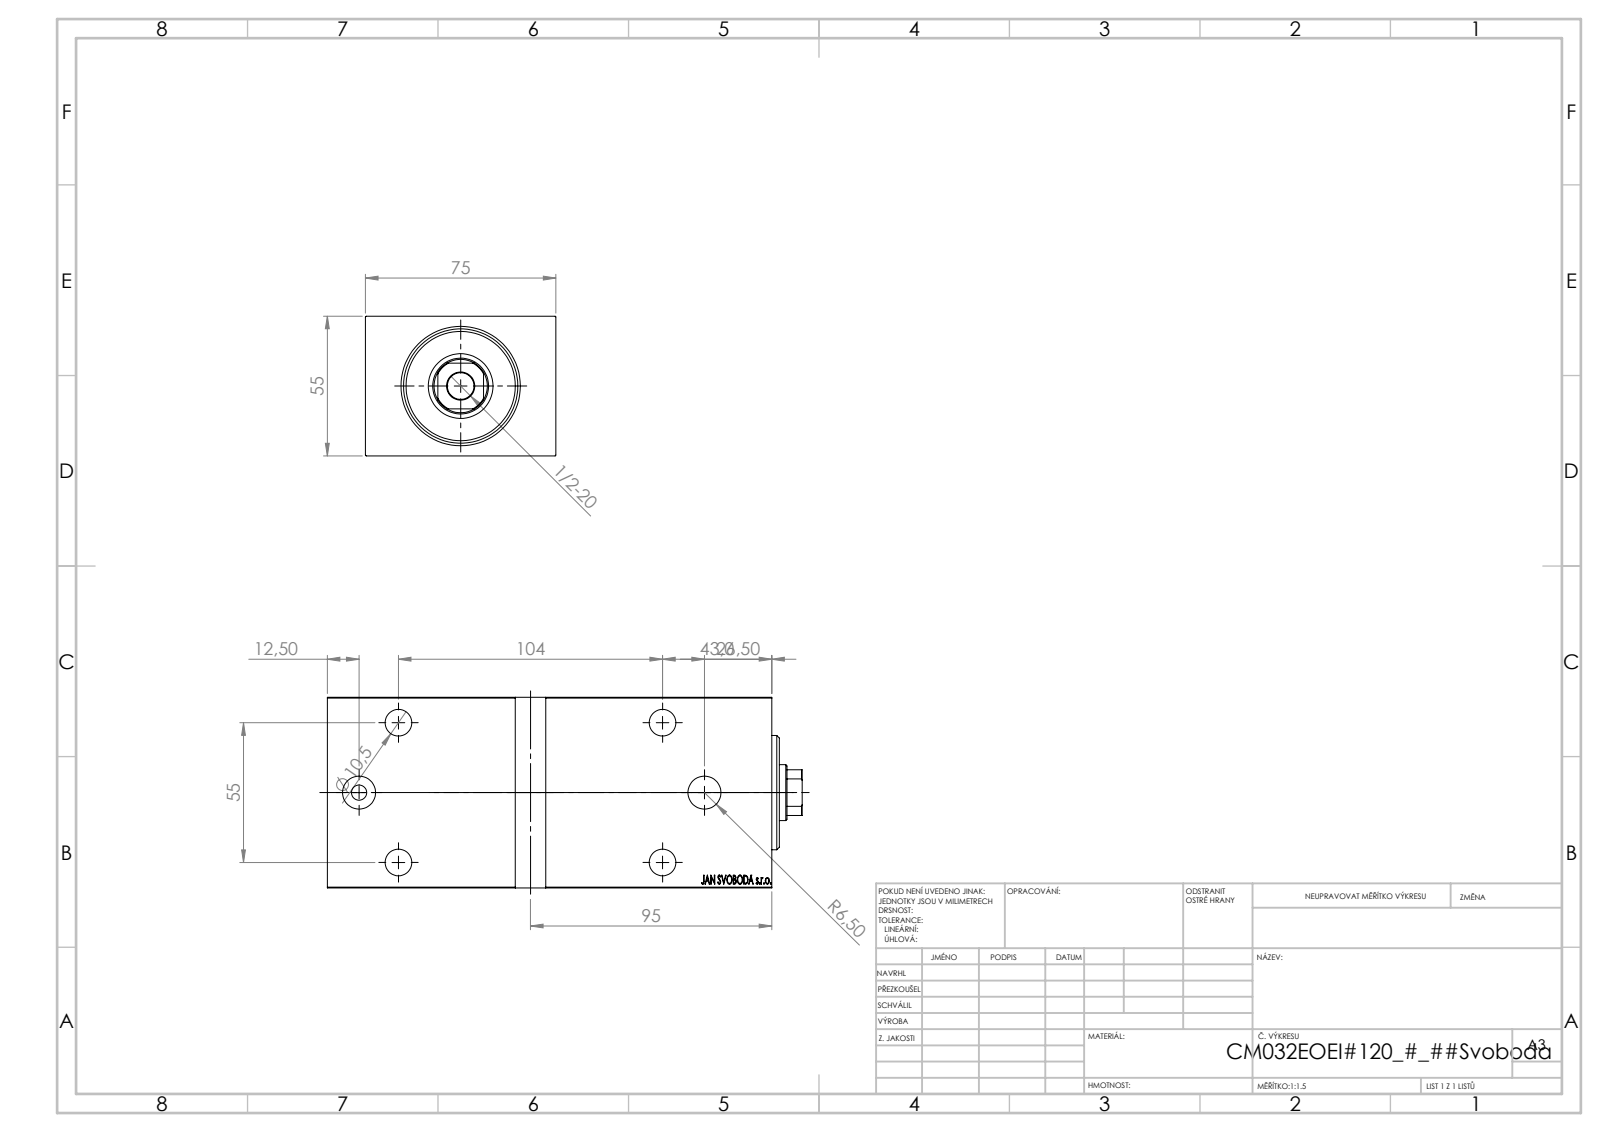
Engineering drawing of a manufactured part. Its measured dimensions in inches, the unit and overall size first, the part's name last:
Units: inches
Overall size (bounding box): 7.362 × 2.953 × 2.165
Round holes (diameter × count): ⌀0.413 ×5, ⌀0.65 ×4, ⌀0.512 ×2, ⌀0.866 ×1, ⌀1.004 ×1, ⌀1.26 ×1, ⌀1.772 ×1
Round bosses / shafts (diameter × count): ⌀1.339 ×1, ⌀0.236 ×1
Partial cylindrical surfaces — rounded edges, fillets, slot ends (radius × count): R0.413 ×1
Main face-to-face distances: 2.165, 2.953, 6.89, 0.118, 0.394, 6.496, 0.197, 6.693, 6.299, 7.008
Hole centre spacings: 1.243, 1.263, 2.165, 4.094, 4.632, 4.828, 4.866, 5.354
Volume: 39.65 in³ · Surface area: 155.3 in²
Bodies: 3 solids, 846 faces (408 planar, 44 cylindrical, 394 other)
Part name (STEP PRODUCT): V450CM_E_Body; V450CM_E_VCP; V450CM_VC_B
STEP written by: SolidWorks 2019 (CONFIG_CONTROL_DESIGN)
